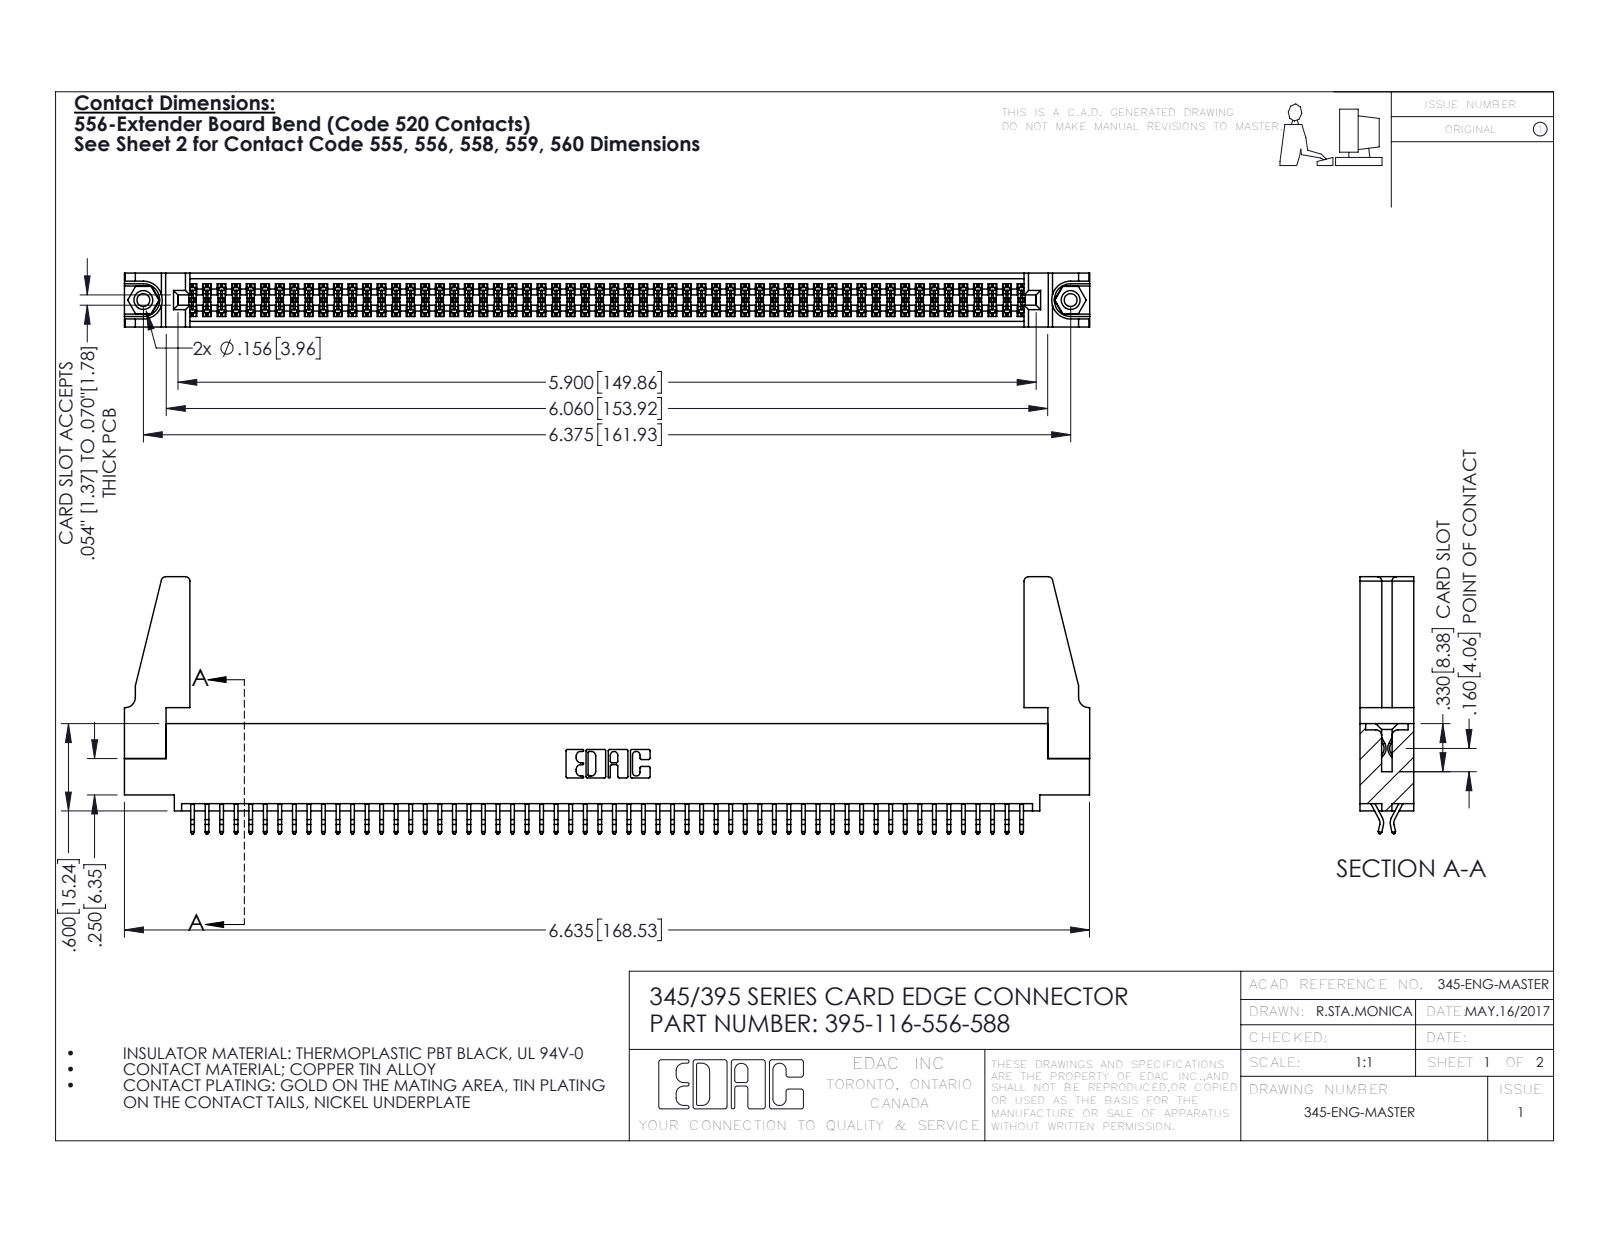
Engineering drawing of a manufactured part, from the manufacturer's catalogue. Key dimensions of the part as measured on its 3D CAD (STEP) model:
Part name (STEP PRODUCT): 345-220-078_345-220-088; 345 Part_0.110 Offset - 0.156 Dia-TH; 345-292-001_556 Tail; 345-250-001_345-250-001-102 (+1 more)
STEP written by: SolidWorks 2016 (CONFIG_CONTROL_DESIGN)
Units: inches
Bodies: 121 solids, 6750 faces (4448 planar, 2286 cylindrical, 16 other)
Overall size (bounding box): 6.636 × 1.767 × 0.37
Volume: 1.202 in³ · Surface area: 42.98 in²
Round holes (diameter × count): ⌀0.089 ×2, ⌀0.125 ×2, ⌀0.156 ×2, ⌀0.064 ×1
Round bosses / shafts (diameter × count): ⌀0.155 ×2
Partial cylindrical surfaces — rounded edges, fillets, slot ends (radius × count): R0.006 ×174, R0.01 ×22, R0.03 ×8, R0.007 ×6, R0.031 ×6, R0.026 ×3, R0.01 ×2, R0.014 ×2
Main face-to-face distances: 0.072, 0.298, 0.37, 0.025, 0.2, 0.098, 0.272, 0.225, 0.175, 0.149
Hole centre spacings: 0.27, 6.139, 6.375
